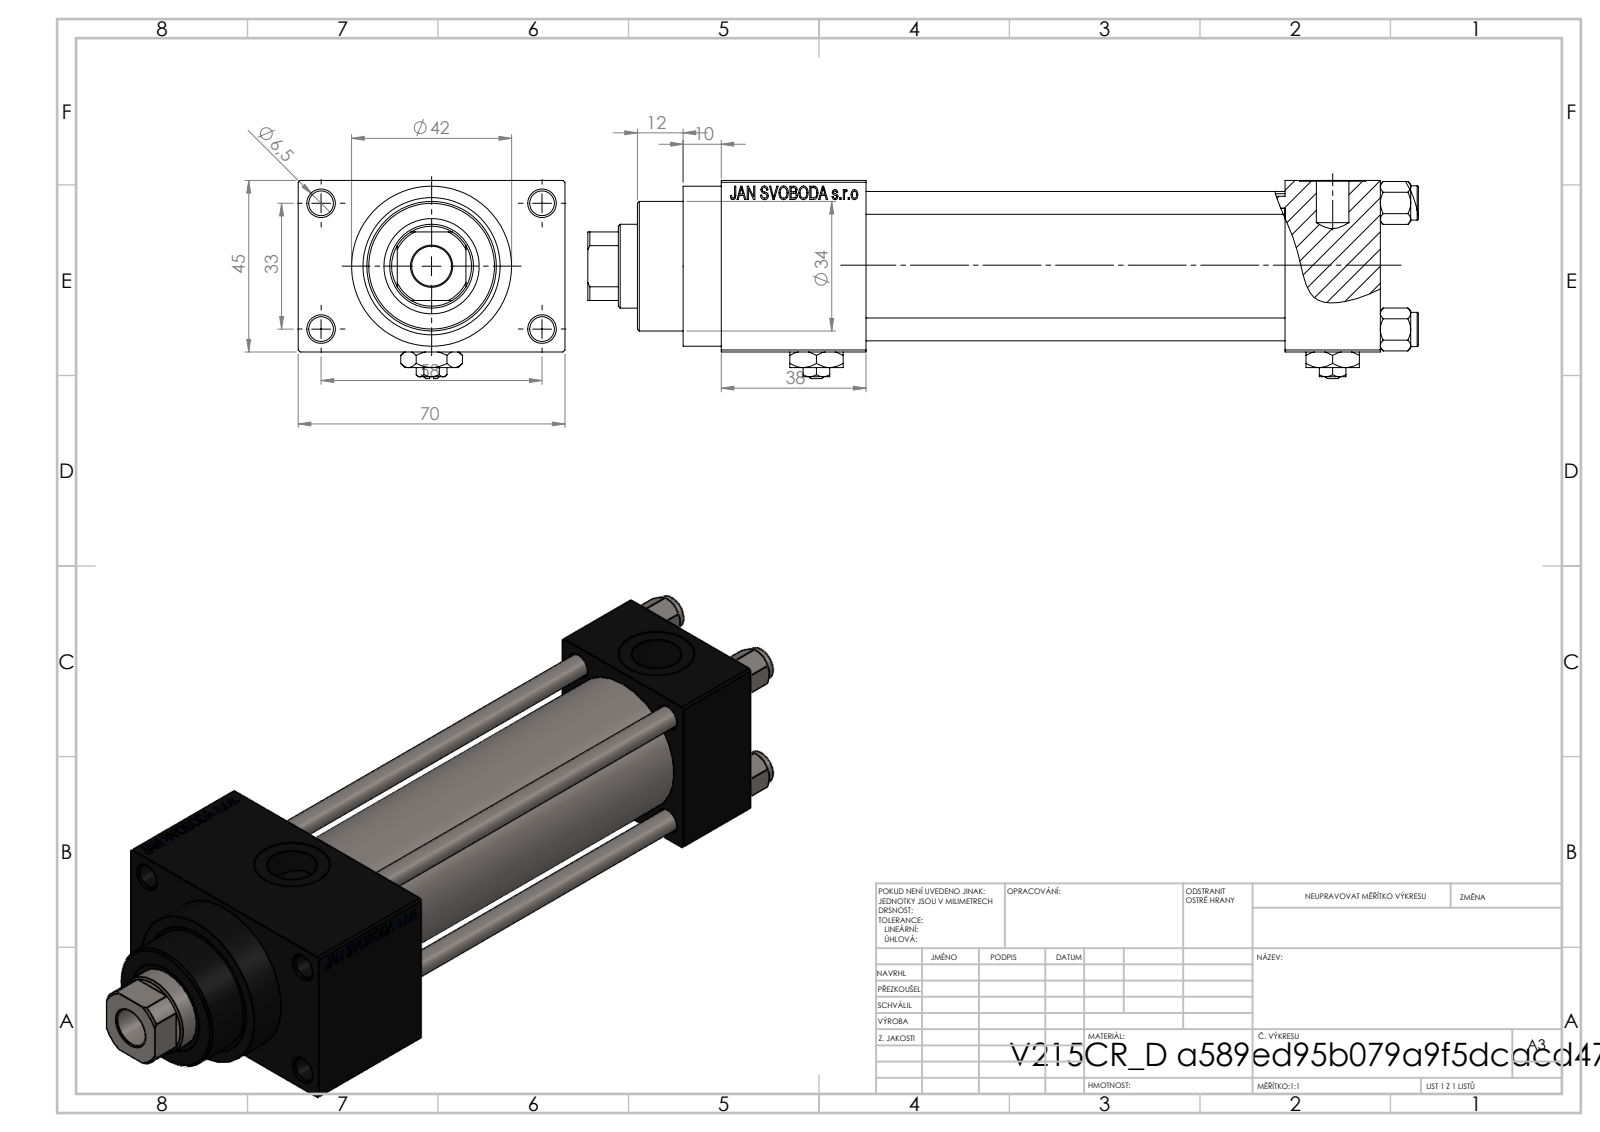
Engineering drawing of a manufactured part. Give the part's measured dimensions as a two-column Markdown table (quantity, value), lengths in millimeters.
| quantity | value |
| --- | --- |
| part name | V215_VC_A; V215CR_VCP_D; NUT_M5_D; Zatka_pro_OIL_PORT (+2 more) |
| STEP written by | SolidWorks 2019 (CONFIG_CONTROL_DESIGN) |
| units | millimeters |
| bodies | 13 solids, 1204 faces (542 planar, 100 cylindrical, 562 other) |
| overall size | 218 × 70 × 52 |
| volume | 292 633 mm³ |
| surface area | 102 977 mm² |
| round holes (diameter × count) | 6 × 4, 6.5 × 4, 7 × 2, 13.16 × 2, 20 × 2, 10.5 × 1, 22 × 1, 24 × 1, 25 × 1, 32 × 1, 33 × 1 |
| round bosses / shafts (diameter × count) | 9 × 4, 42 × 1, 38 × 1, 34 × 1 |
| partial cylindrical surfaces (radius × count) | 10.5 × 1 |
| main face-to-face distances | 45, 25, 12.5, 57.5, 110, 135, 148, 38, 70, 173 |
| hole center spacings | 12.4, 23.48, 33.2, 33.37, 35.35, 45.6, 56.35, 33 |
